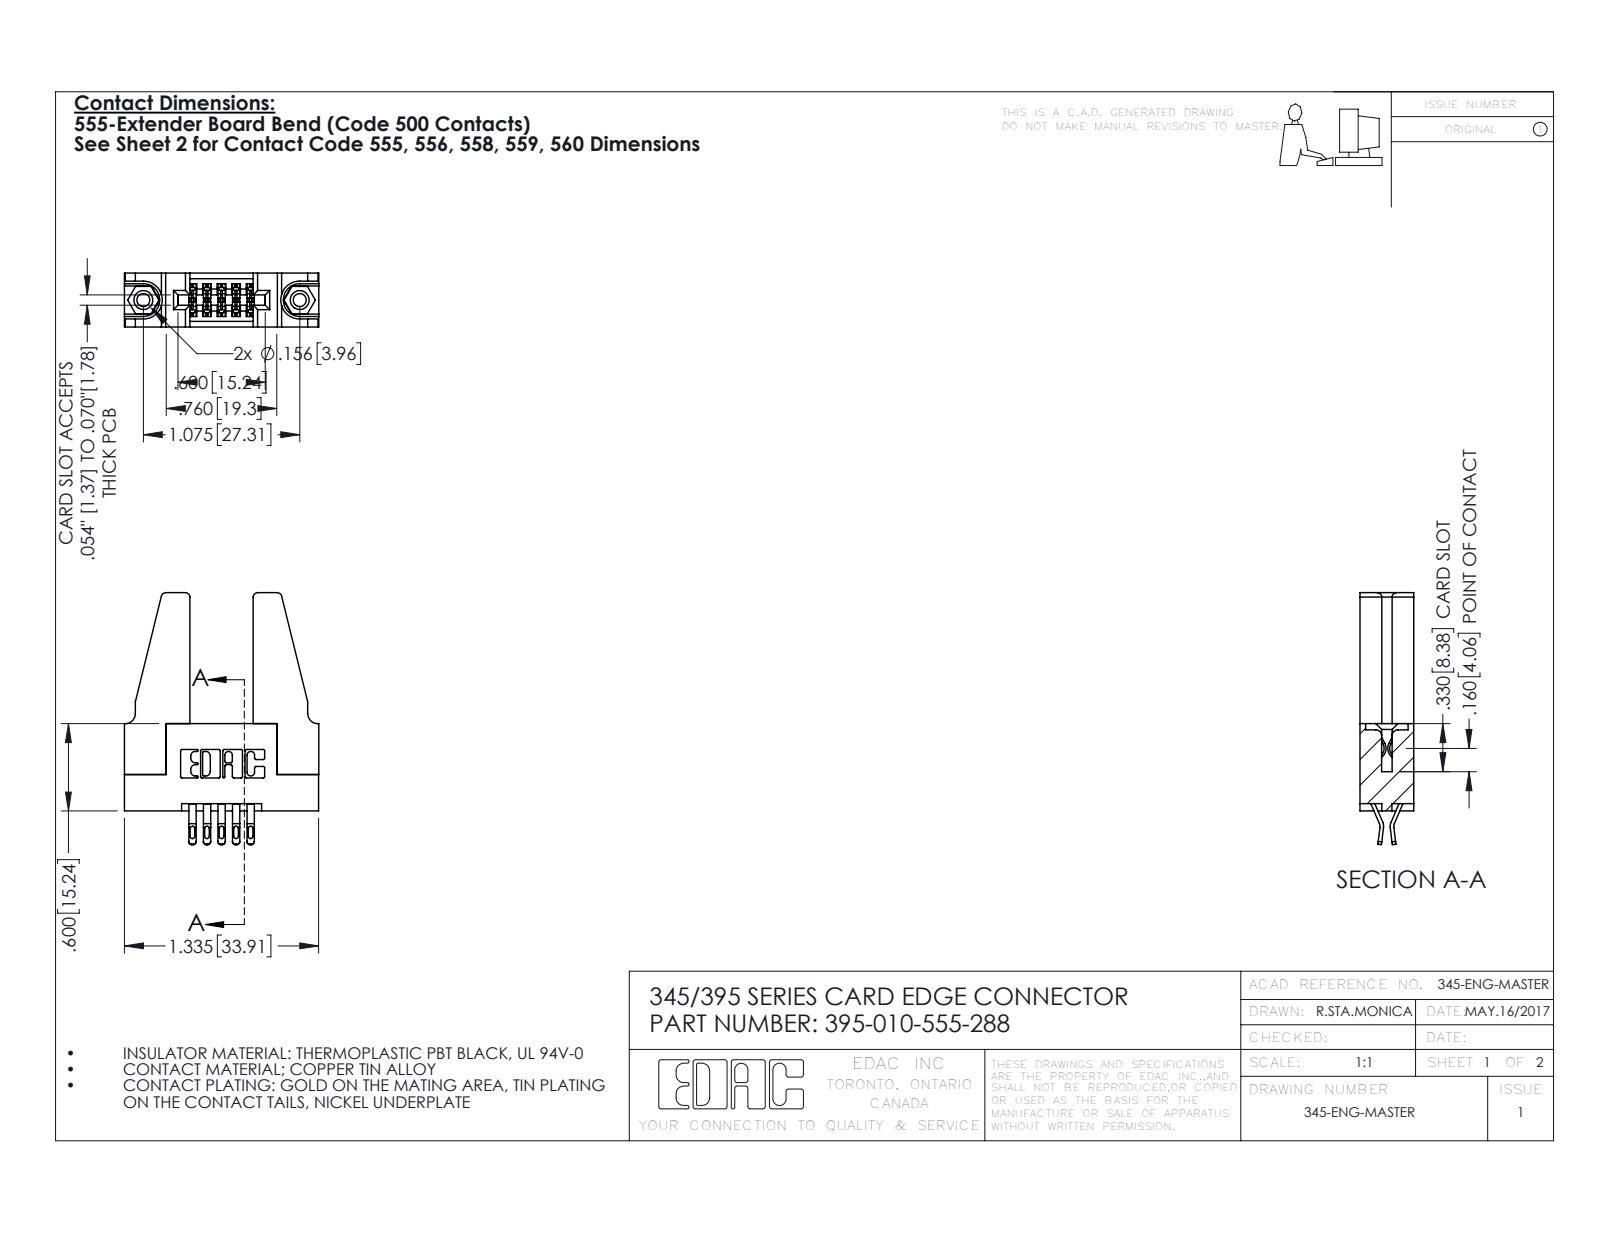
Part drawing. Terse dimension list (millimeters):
name: 345-250-001_345-250-001-102; 395-010-555-288; 345-292-001_555 Tail; 345 Part_Flush Mounting Lugs - 0.156 Dia-TH (+1 more)
written by: SolidWorks 2016 (CONFIG_CONTROL_DESIGN)
unit: mm
bodies: 15 solids, 810 faces (462 planar, 332 cylindrical, 16 other)
size: 44 × 33.9 × 9.4
volume: 6 230 mm³; area: 6 916 mm²
holes: 2× ⌀2.3, 2× ⌀3.2, 2× ⌀4, 1× ⌀1.6
bosses: 2× ⌀3.9
rounds: 25× R0.4, 22× R0.3, 20× R0.5, 15× R0.2, 8× R0.8, 6× R0.2, 6× R0.8, 3× R0.7
face distances: 9.4, 1.8, 5.1, 7.6, 15.2, 6.4, 3.8, 3.8, 8.9, 0.6
hole spacings: 6.9, 21.5, 27.3
